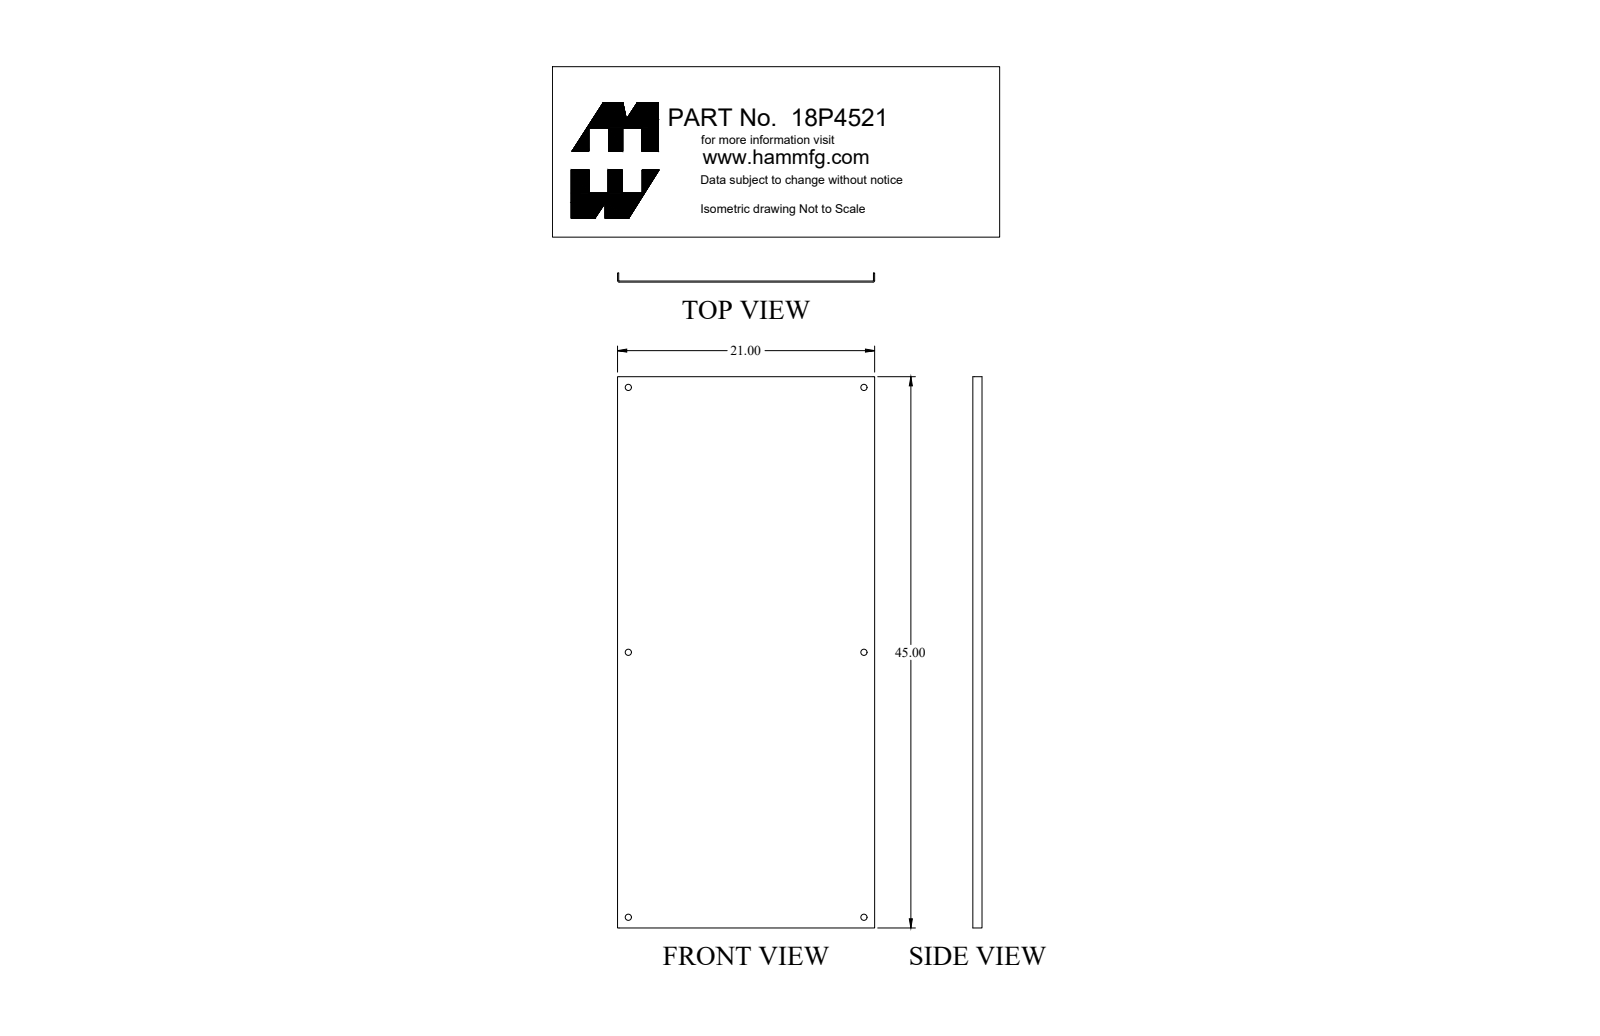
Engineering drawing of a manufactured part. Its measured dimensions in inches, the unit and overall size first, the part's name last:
Units: inches
Overall size (bounding box): 45 × 21 × 0.75
Round holes (diameter × count): ⌀0.5 ×6
Partial cylindrical surfaces — rounded edges, fillets, slot ends (radius × count): R0.03 ×2, R0.125 ×2
Main face-to-face distances: 0.095, 20.905, 20.81, 21, 0.75, 0.655, 45
Hole centre spacings: 21.625, 28.951, 19.25, 43.25, 47.34
Volume: 94.98 in³ · Surface area: 2 013 in²
Bodies: 1 solid, 26 faces (10 planar, 16 cylindrical, 0 other)
Part name (STEP PRODUCT): 18P4521_Default
STEP written by: SolidWorks 2018 (CONFIG_CONTROL_DESIGN)
